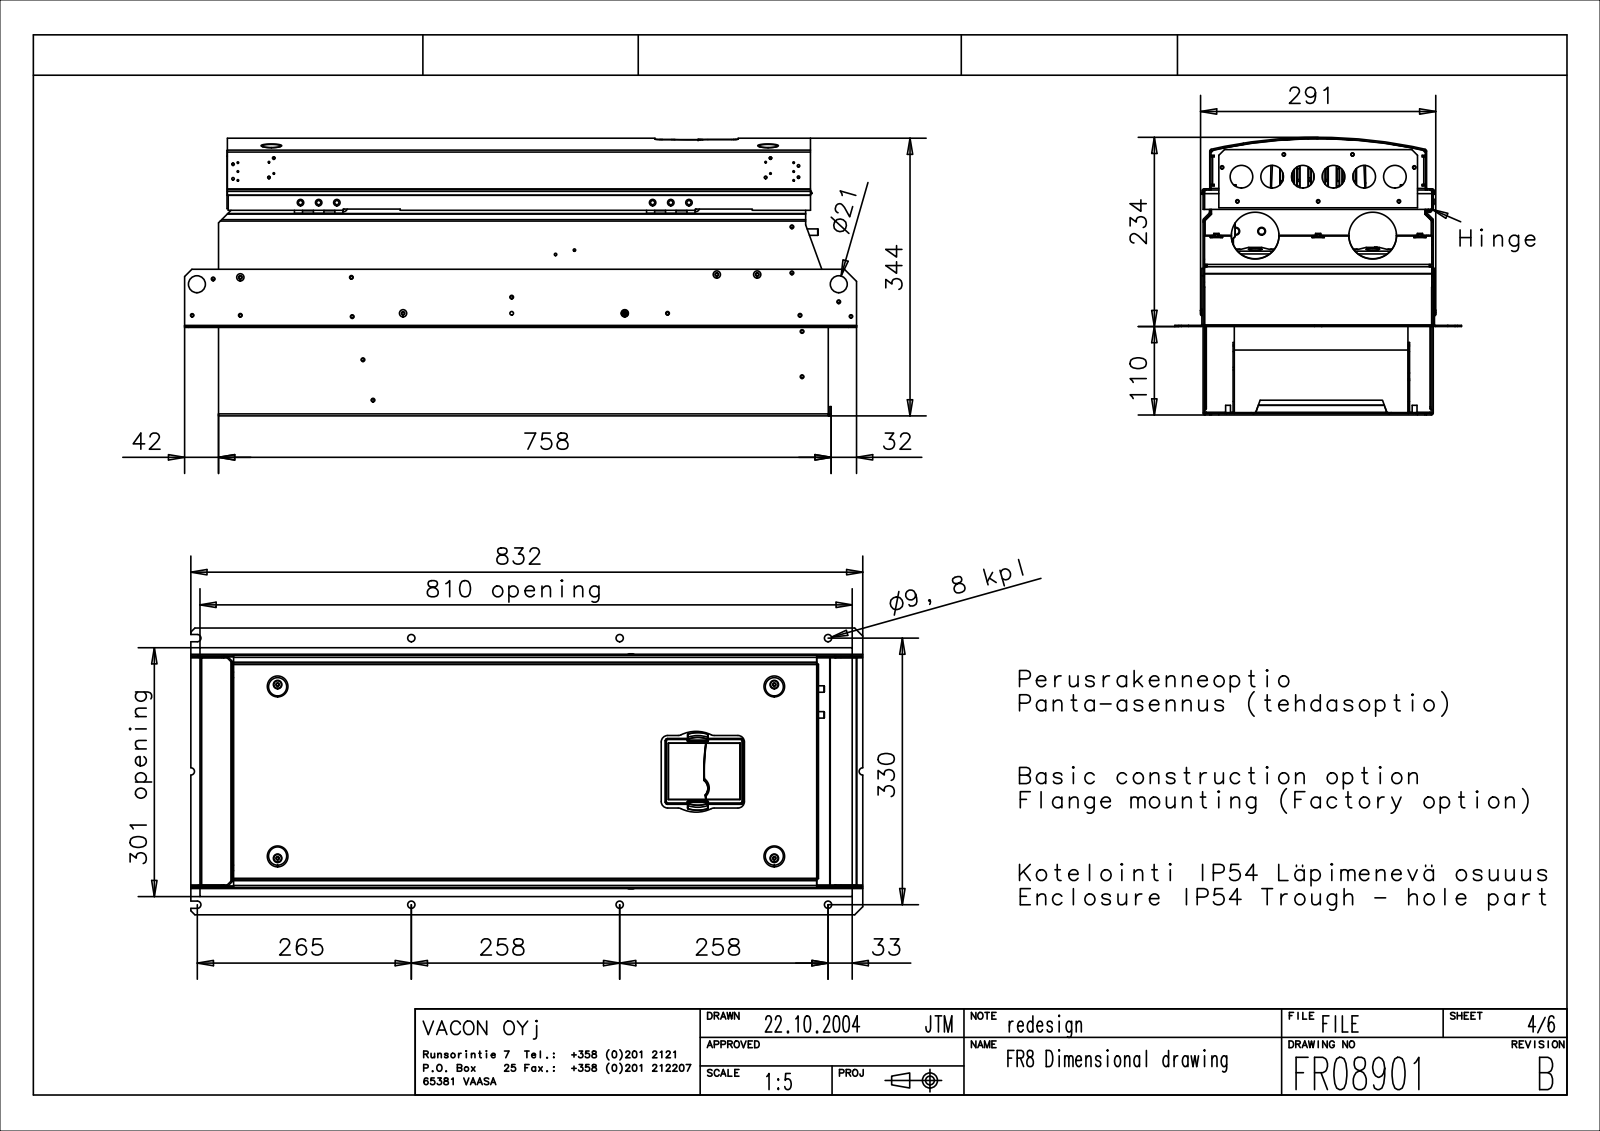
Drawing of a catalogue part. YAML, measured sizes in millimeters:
part_name: "PRT0003"
step_written_by: "CREO PARAMETRIC BY PTC INC, 2018070 (CONFIG_CONTROL_DESIGN)"
units: millimeters
bodies: {solids: 65, faces: 5643, planar: 1913, cylindrical: 3189, other: 541}
overall_size: [832, 355, 343.73]
volume: 475654
surface_area: 4393000
round_holes:
  - {diameter: 8, count: 571}
  - {diameter: 3.4, count: 89}
  - {diameter: 4.5, count: 23}
  - {diameter: 3.1, count: 18}
  - {diameter: 3.3, count: 15}
  - {diameter: 2, count: 14}
  - {diameter: 3, count: 12}
  - {diameter: 4.2, count: 12}
  - {diameter: 9, count: 11}
  - {diameter: 5.4, count: 9}
  - {diameter: 28, count: 9}
  - {diameter: 4, count: 8}
round_bosses_or_shafts:
  - {diameter: 5.5, count: 15}
  - {diameter: 6.4, count: 14}
  - {diameter: 4, count: 11}
  - {diameter: 1, count: 9}
  - {diameter: 5.4, count: 7}
  - {diameter: 3, count: 3}
  - {diameter: 8.75, count: 2}
  - {diameter: 8, count: 2}
partial_cylinders:
  - {radius: 3.5, count: 106}
  - {radius: 0.2, count: 99}
  - {radius: 1, count: 93}
  - {radius: 2.5, count: 74}
  - {radius: 0.15, count: 58}
  - {radius: 1.5, count: 41}
  - {radius: 2, count: 31}
  - {radius: 0.5, count: 21}
face_to_face_distances: [1.5, 283.5, 277, 285, 282, 3, 275.5, 278.5, 109.5, 167.5]
hole_center_spacings: [9.2, 18.4, 27.6, 36.8, 46, 55.2, 64.4, 73.6]
